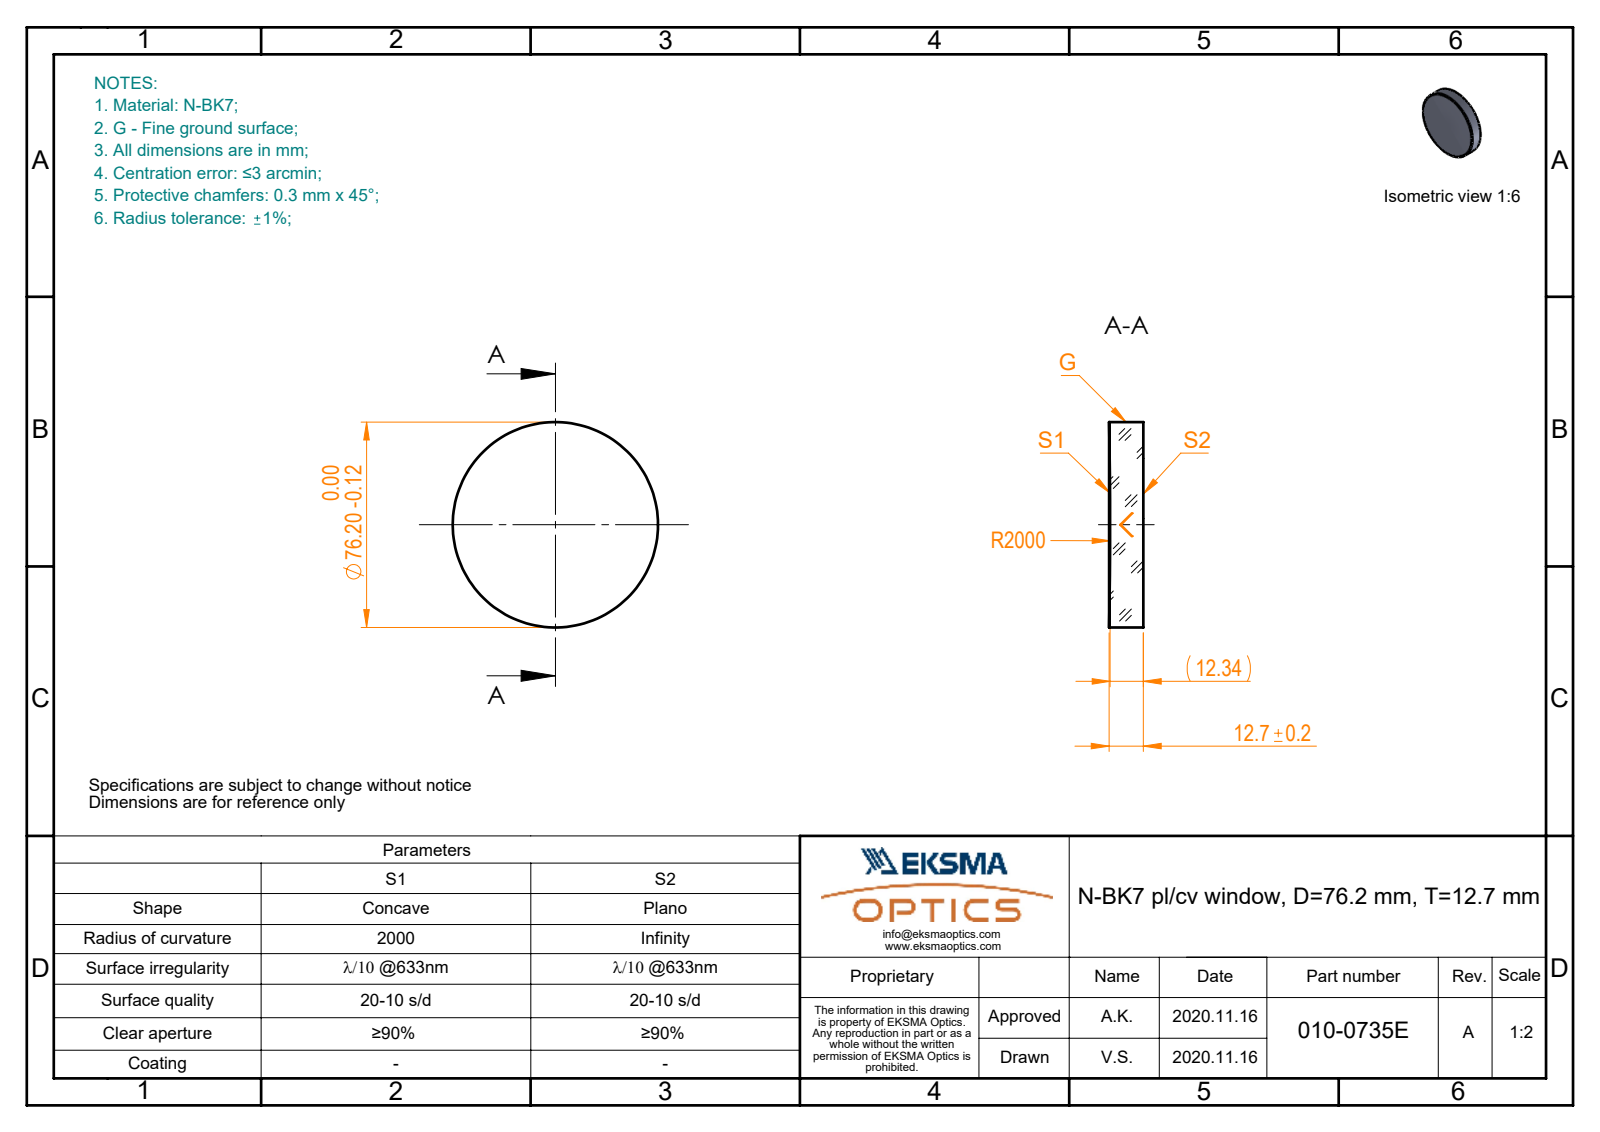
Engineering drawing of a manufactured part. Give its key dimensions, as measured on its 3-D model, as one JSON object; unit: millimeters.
{"part_name": "010-0735E_N-BK7_PCV_window", "step_written_by": "SolidWorks 2019 (CONFIG_CONTROL_DESIGN)", "units": "millimeters", "bodies": {"solids": 1, "faces": 5, "planar": 1, "cylindrical": 2, "other": 2}, "overall_size": [76.2, 76.2, 12.7], "volume_mm3": 57089, "surface_area_mm2": 12161, "round_bosses_or_shafts": [[76.2, 1]]}
